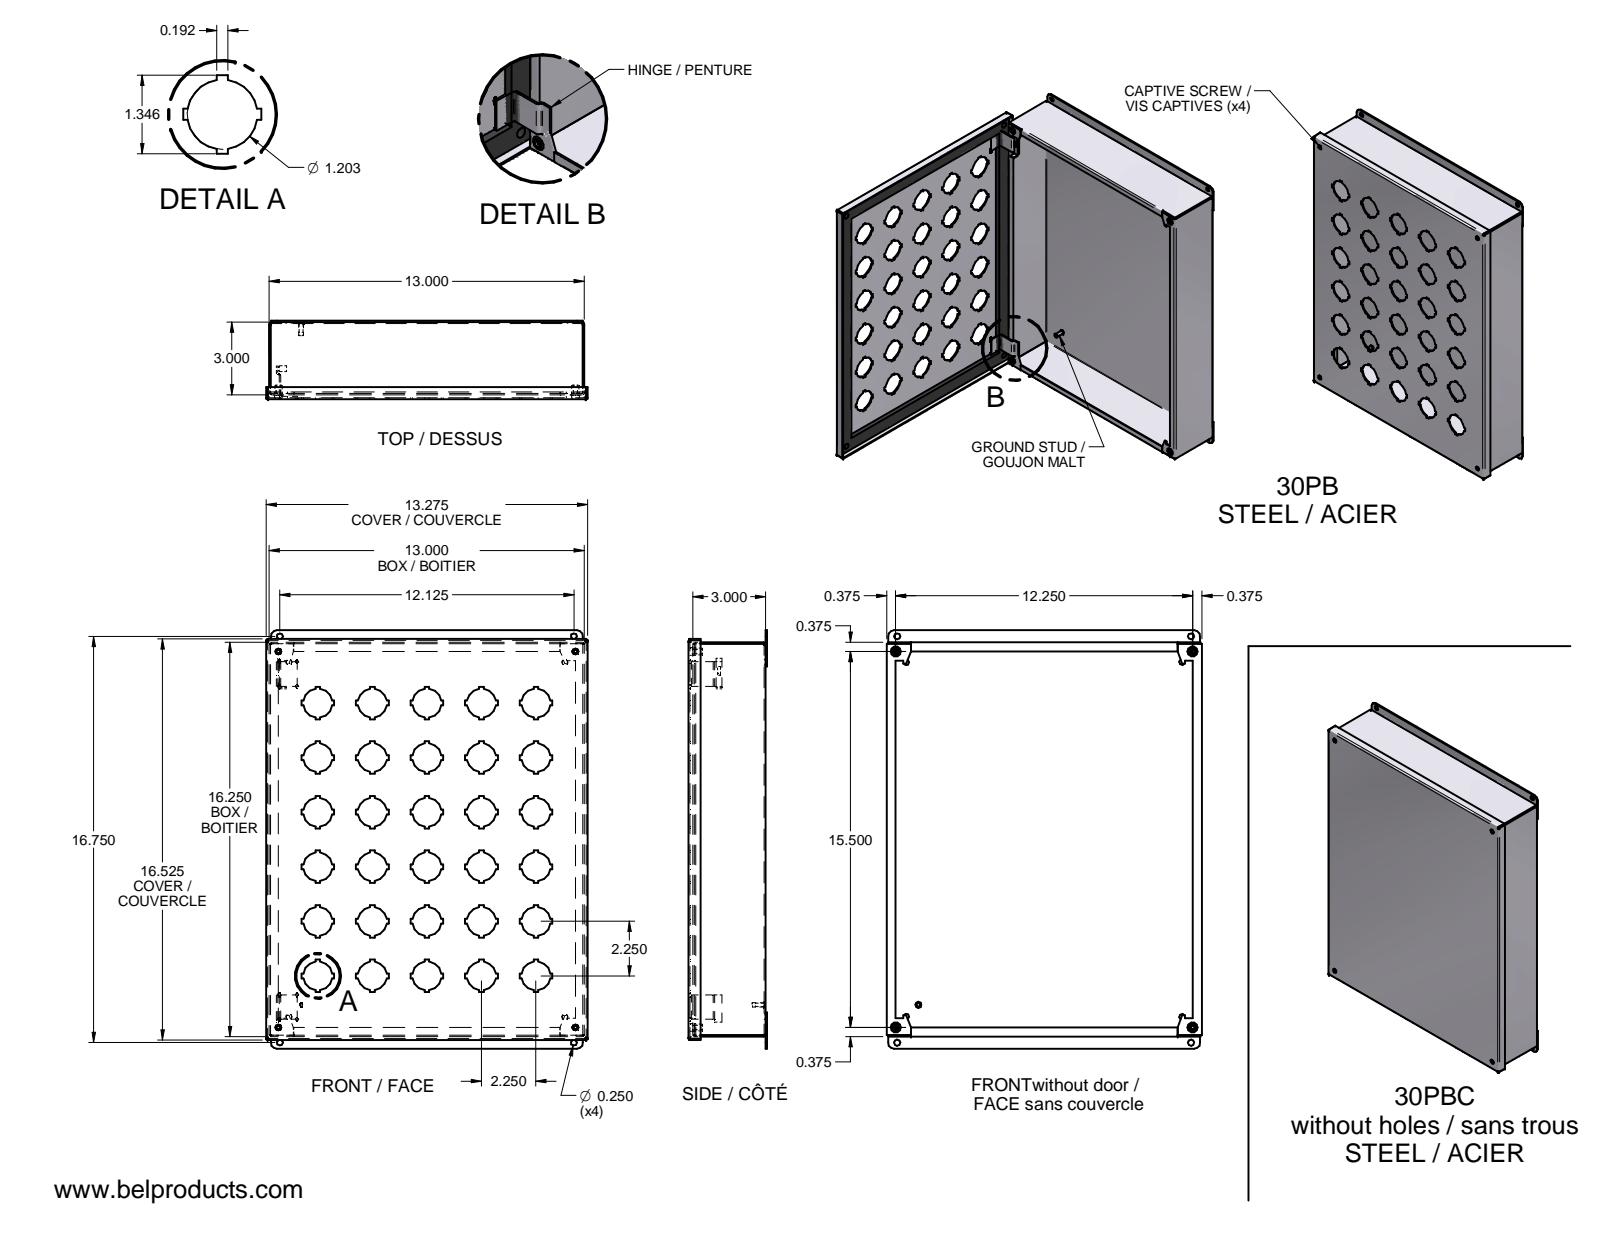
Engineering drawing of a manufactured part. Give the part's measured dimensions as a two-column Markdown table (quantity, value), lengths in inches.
| quantity | value |
| --- | --- |
| part name | 30PBC_COUVERCLE; 30PBC-C; 30PBC_GASKET; PB-PENTURE-1 (+7 more) |
| STEP written by | Unknown (AUTOMOTIVE_DESIGN) |
| units | inches |
| bodies | 13 solids, 1286 faces (899 planar, 106 cylindrical, 281 other) |
| overall size | 17.25 × 13.275 × 3.245 |
| volume | 51.66 in³ |
| surface area | 1 504 in² |
| round holes (diameter × count) | 0.125 × 9, 0.25 × 8, 0.159 × 4, 0.216 × 4, 0.245 × 4, 0.265 × 4, 0.29 × 4, 0.312 × 4, 0.136 × 1 |
| round bosses / shafts (diameter × count) | 0.119 × 9, 0.296 × 4, 0.25 × 4, 0.256 × 1, 0.19 × 1, 0.02 × 1 |
| partial cylindrical surfaces (radius × count) | 0.032 × 16, 0.092 × 16, 0.25 × 4, 0.063 × 2 |
| main face-to-face distances | 0.06, 3.125, 3.185, 3.065, 12.94, 0.06, 16.19, 0.137, 13, 12.88 |
| hole center spacings | 0.619, 0.628, 0.736, 1.01, 1.126, 1.25, 11.798, 11.82 |
